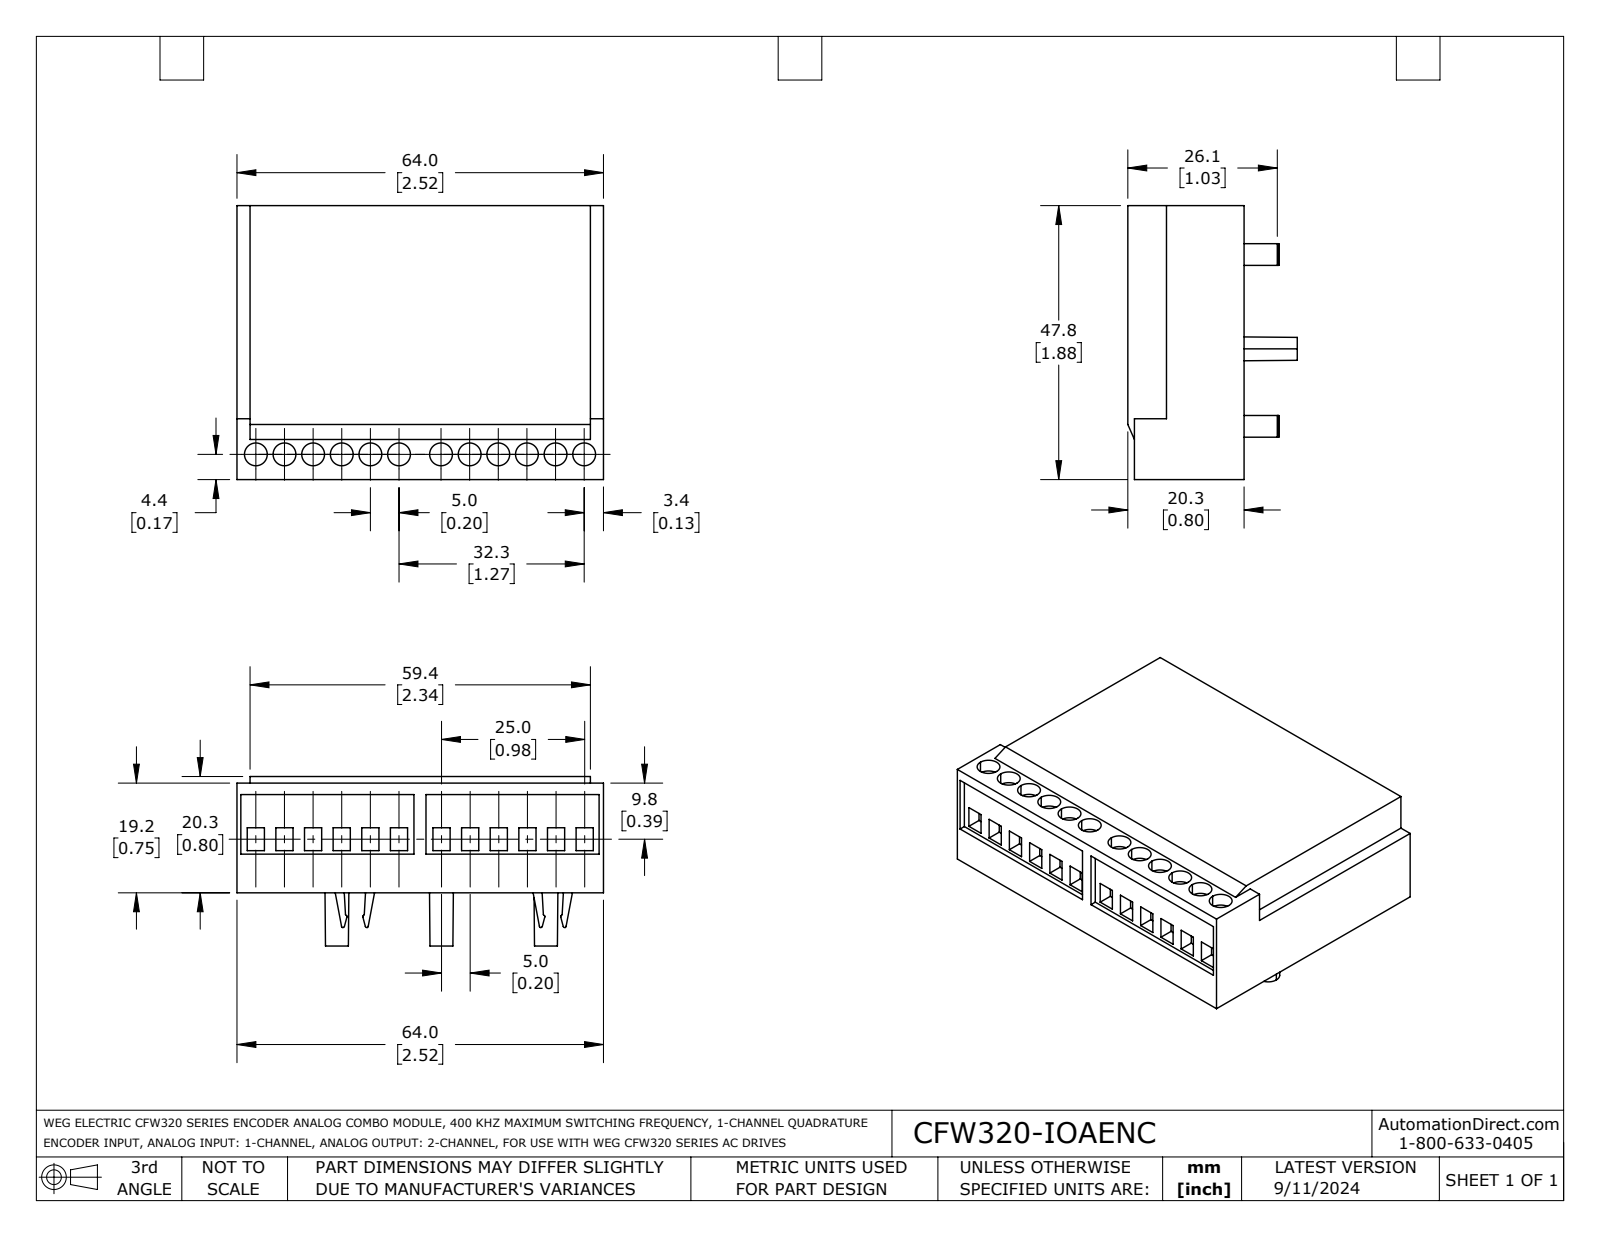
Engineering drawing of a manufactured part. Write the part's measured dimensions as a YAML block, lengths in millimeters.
part_name: "CFW320 IOAENC"
step_written_by: "SolidWorks 2021 (AUTOMOTIVE_DESIGN)"
units: millimeters
bodies: {solids: 1, faces: 204, planar: 158, cylindrical: 24, other: 22}
overall_size: [64, 47.8, 29.6]
volume: 58120
surface_area: 12320
round_holes:
  - {diameter: 4, count: 12}
face_to_face_distances: [20.3, 47.8, 64, 2.3, 61.7, 1.1, 46.8, 4.2, 16.1, 19.2]
hole_center_spacings: [5, 10, 15, 32.3, 27.3, 37.3, 20, 22.3]
